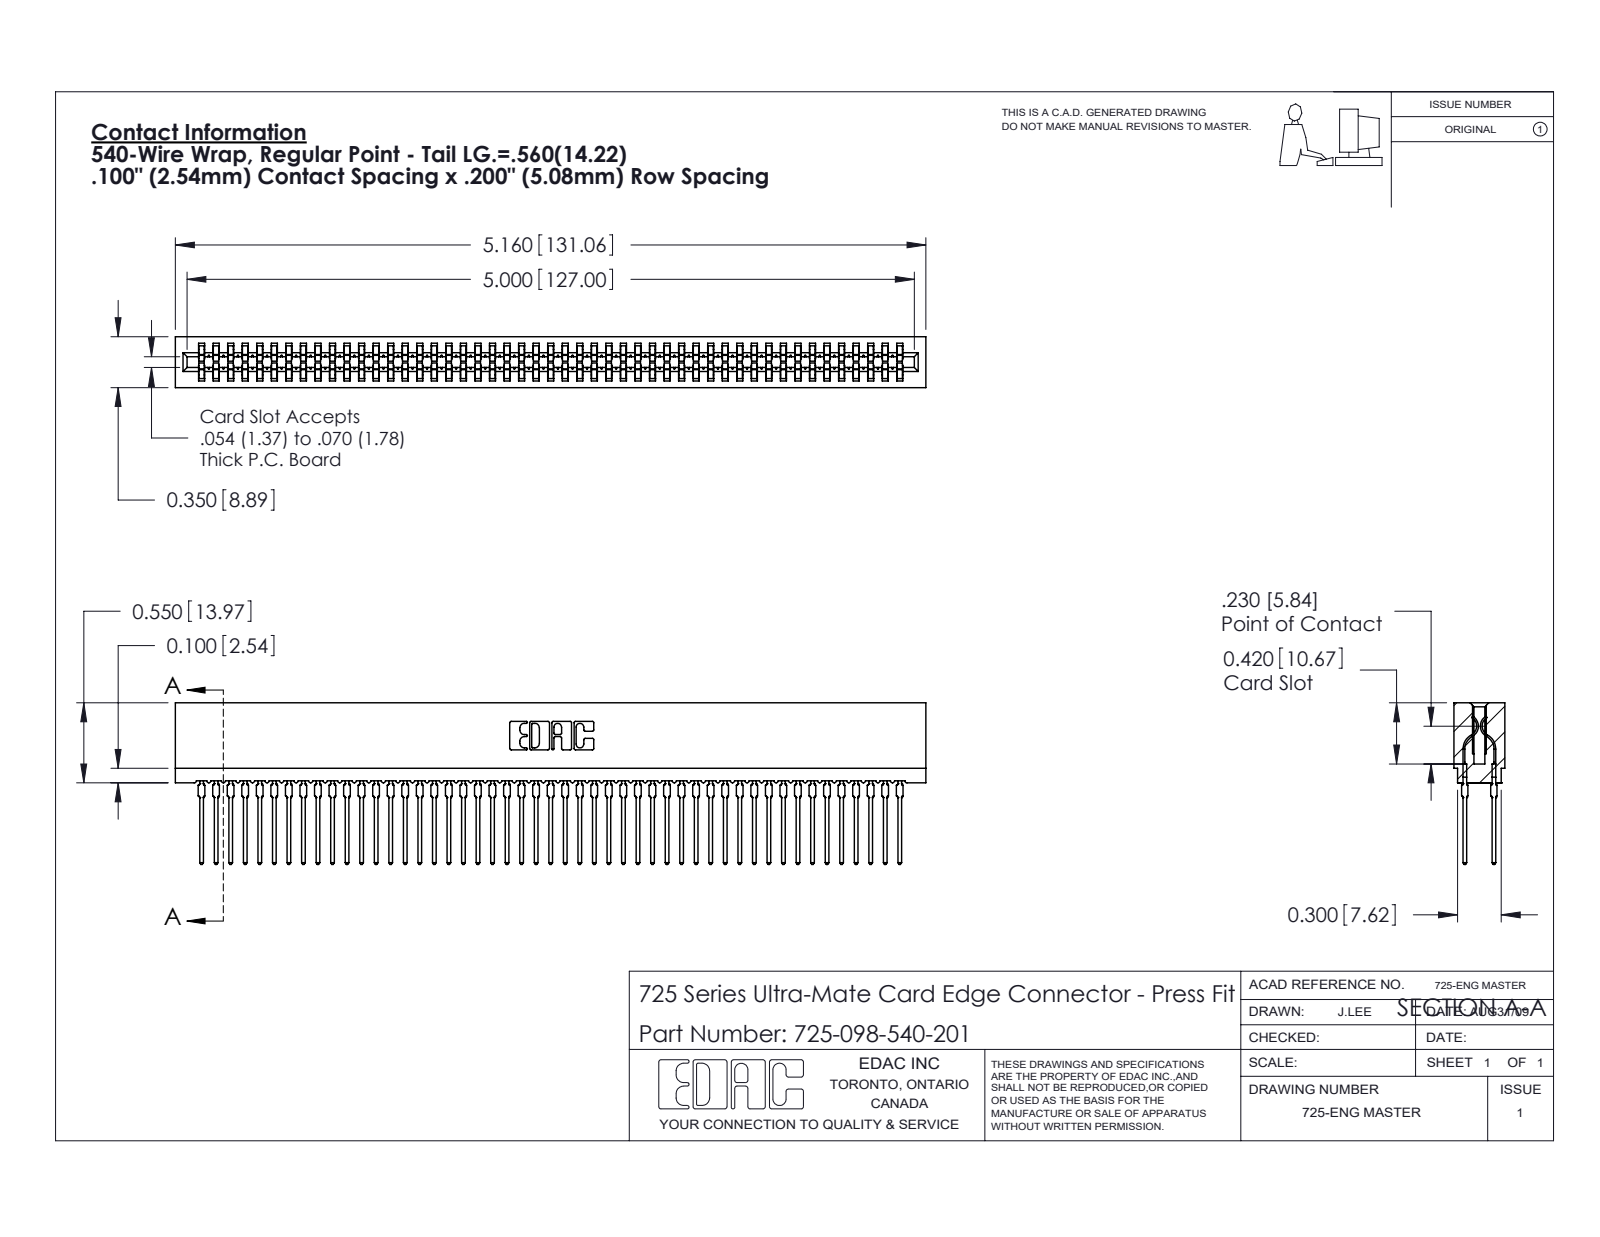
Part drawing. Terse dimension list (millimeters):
name: 725-098-540-201; 725 Part_Insulator Option - 01; 745-292-001_540
written by: SolidWorks 2020 (CONFIG_CONTROL_DESIGN)
unit: mm
bodies: 99 solids, 8866 faces (4563 planar, 1755 cylindrical, 2548 other)
size: 131.1 × 28.2 × 8.9
volume: 10 700 mm³; area: 23 780 mm²
rounds: 196× R0.5, 98× R0.4, 22× R0.3, 8× R0.1, 8× R0.3, 6× R0.2, 6× R0.8, 3× R0.7
face distances: 5.1, 1.6, 7.3, 8.9, 5.4, 3.5, 1.9, 3.8, 2.2, 6.7
